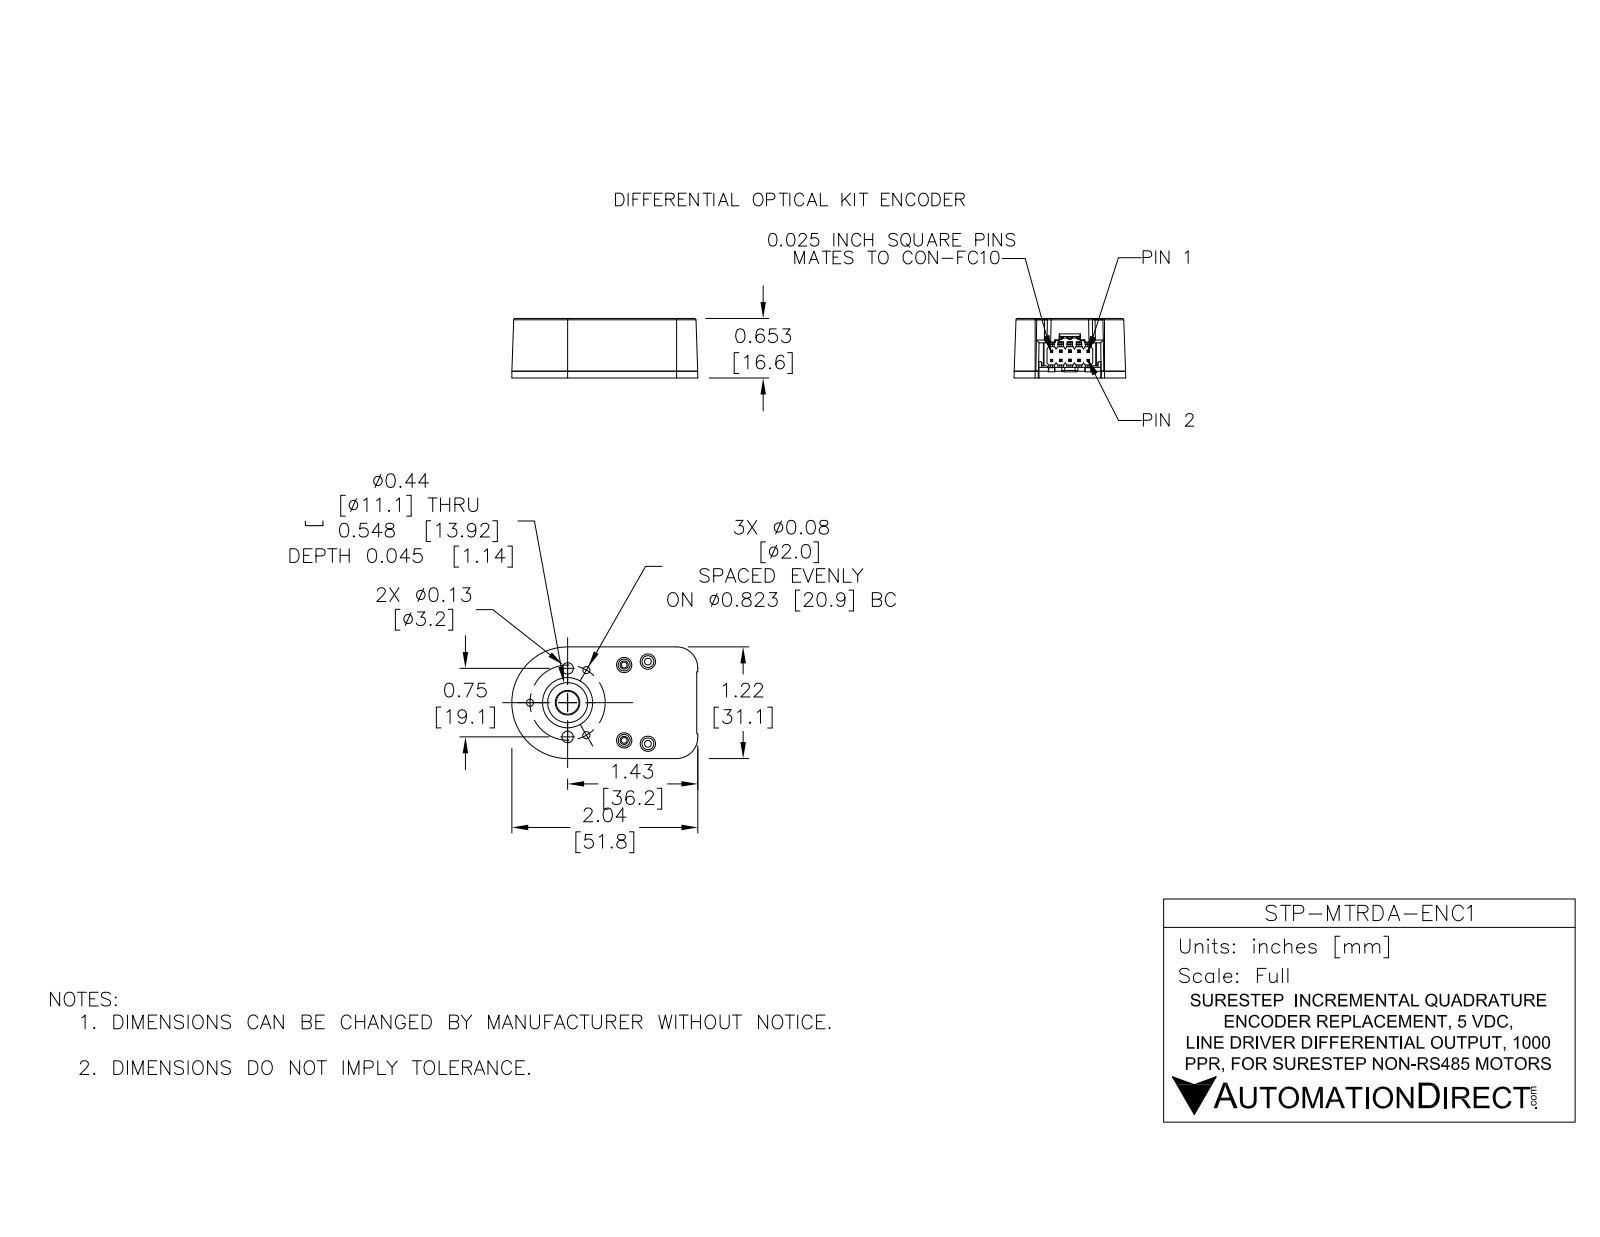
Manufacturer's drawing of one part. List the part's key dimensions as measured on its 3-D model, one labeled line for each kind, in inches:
Part name (STEP PRODUCT): STP-MTRA-ENC1
STEP written by: SolidWorks 2017 (AUTOMOTIVE_DESIGN)
Units: inches
Bodies: 29 solids, 1685 faces (780 planar, 424 cylindrical, 481 other)
Overall size (bounding box): 2.038 × 1.223 × 0.653
Volume: 0.762 in³ · Surface area: 20.73 in²
Round holes (diameter × count): ⌀0.032 ×5, ⌀0.089 ×4, ⌀0.13 ×4, ⌀0.078 ×3, ⌀0.125 ×2, ⌀0.093 ×1, ⌀0.197 ×1
Round bosses / shafts (diameter × count): ⌀0.078 ×5, ⌀0.187 ×4, ⌀0.16 ×4, ⌀0.096 ×4, ⌀0.112 ×3, ⌀0.195 ×2, ⌀0.52 ×1, ⌀0.487 ×1
Partial cylindrical surfaces — rounded edges, fillets, slot ends (radius × count): R0.025 ×46, R0.016 ×37, R0.005 ×14, R0.008 ×14, R0.02 ×10, R0.031 ×8, R0.015 ×6, R0.03 ×6
Main face-to-face distances: 0.653, 0.06, 0.113, 0.135, 0.54, 0.405, 0.518, 0.075, 0.1, 0.075
Hole centre spacings: 0.1, 0.2, 0.411, 0.713, 0.207, 0.263, 0.3, 0.375
